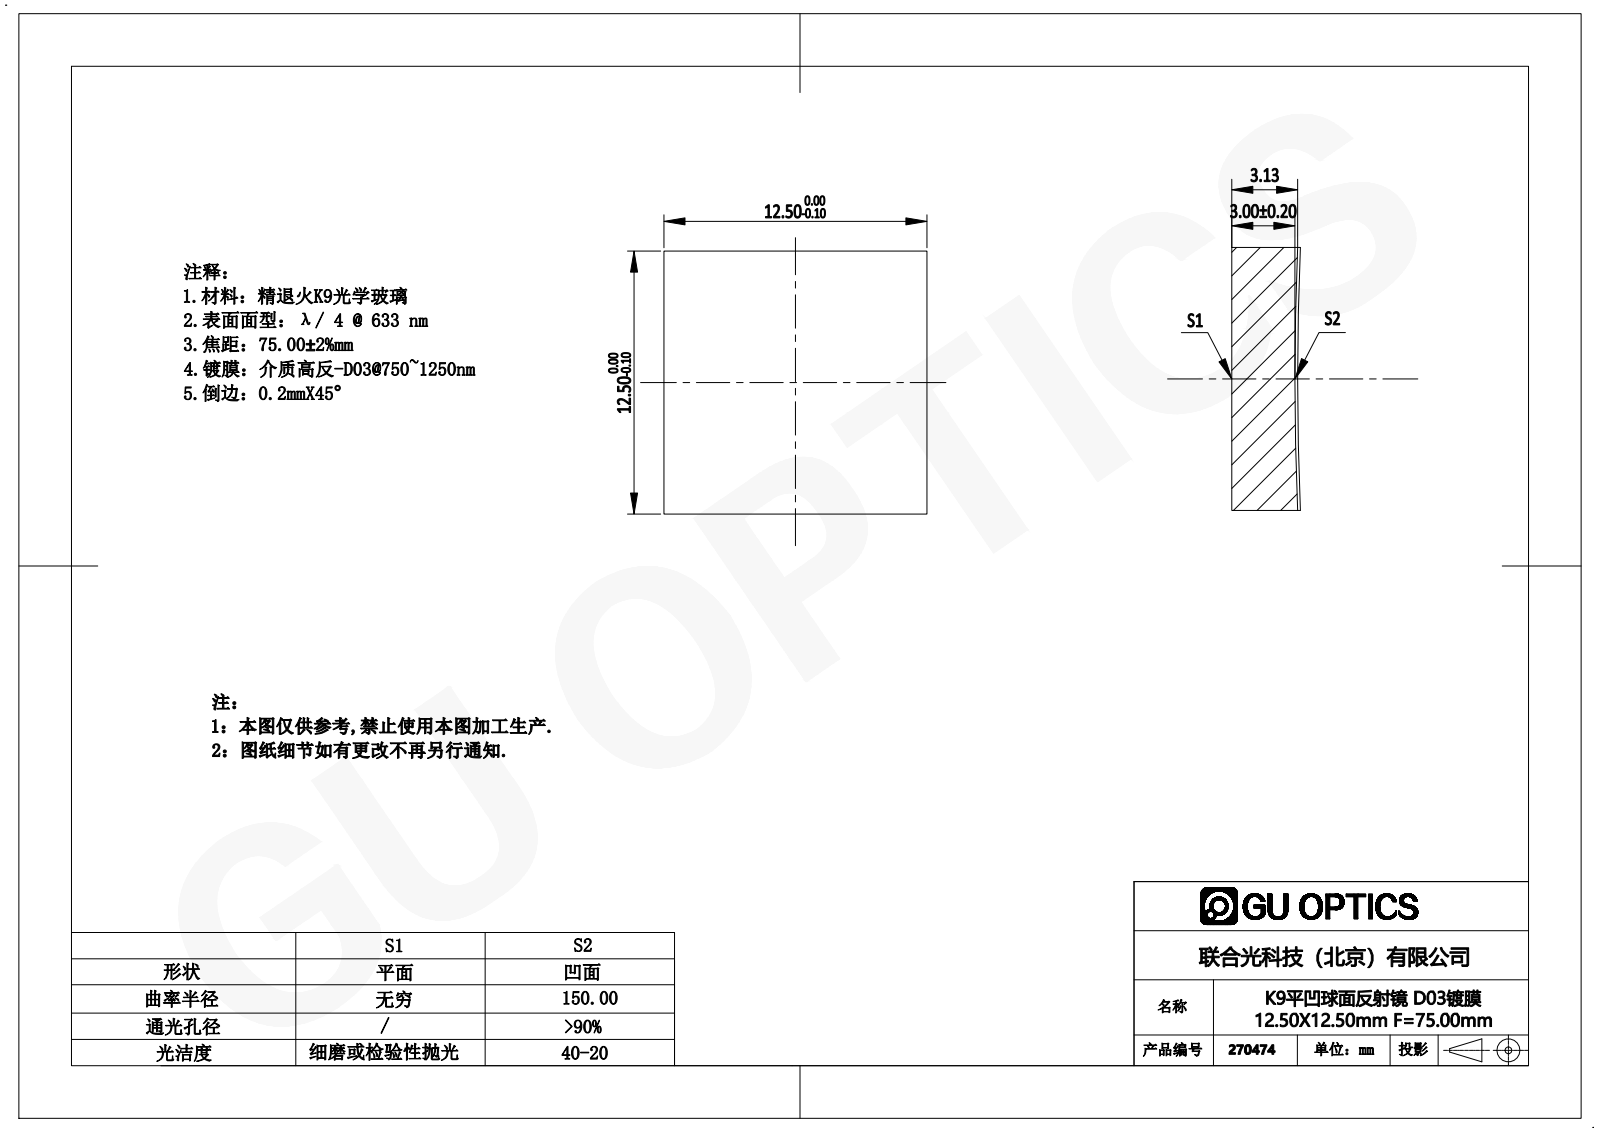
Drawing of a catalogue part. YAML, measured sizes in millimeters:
part_name: "270019"
step_written_by: "SolidWorks 2019 (AUTOMOTIVE_DESIGN)"
units: millimeters
bodies: {solids: 1, faces: 7, planar: 5, cylindrical: 0, other: 2}
overall_size: [12.5, 12.5, 3.26]
volume: 482
surface_area: 471
face_to_face_distances: [12.5]
